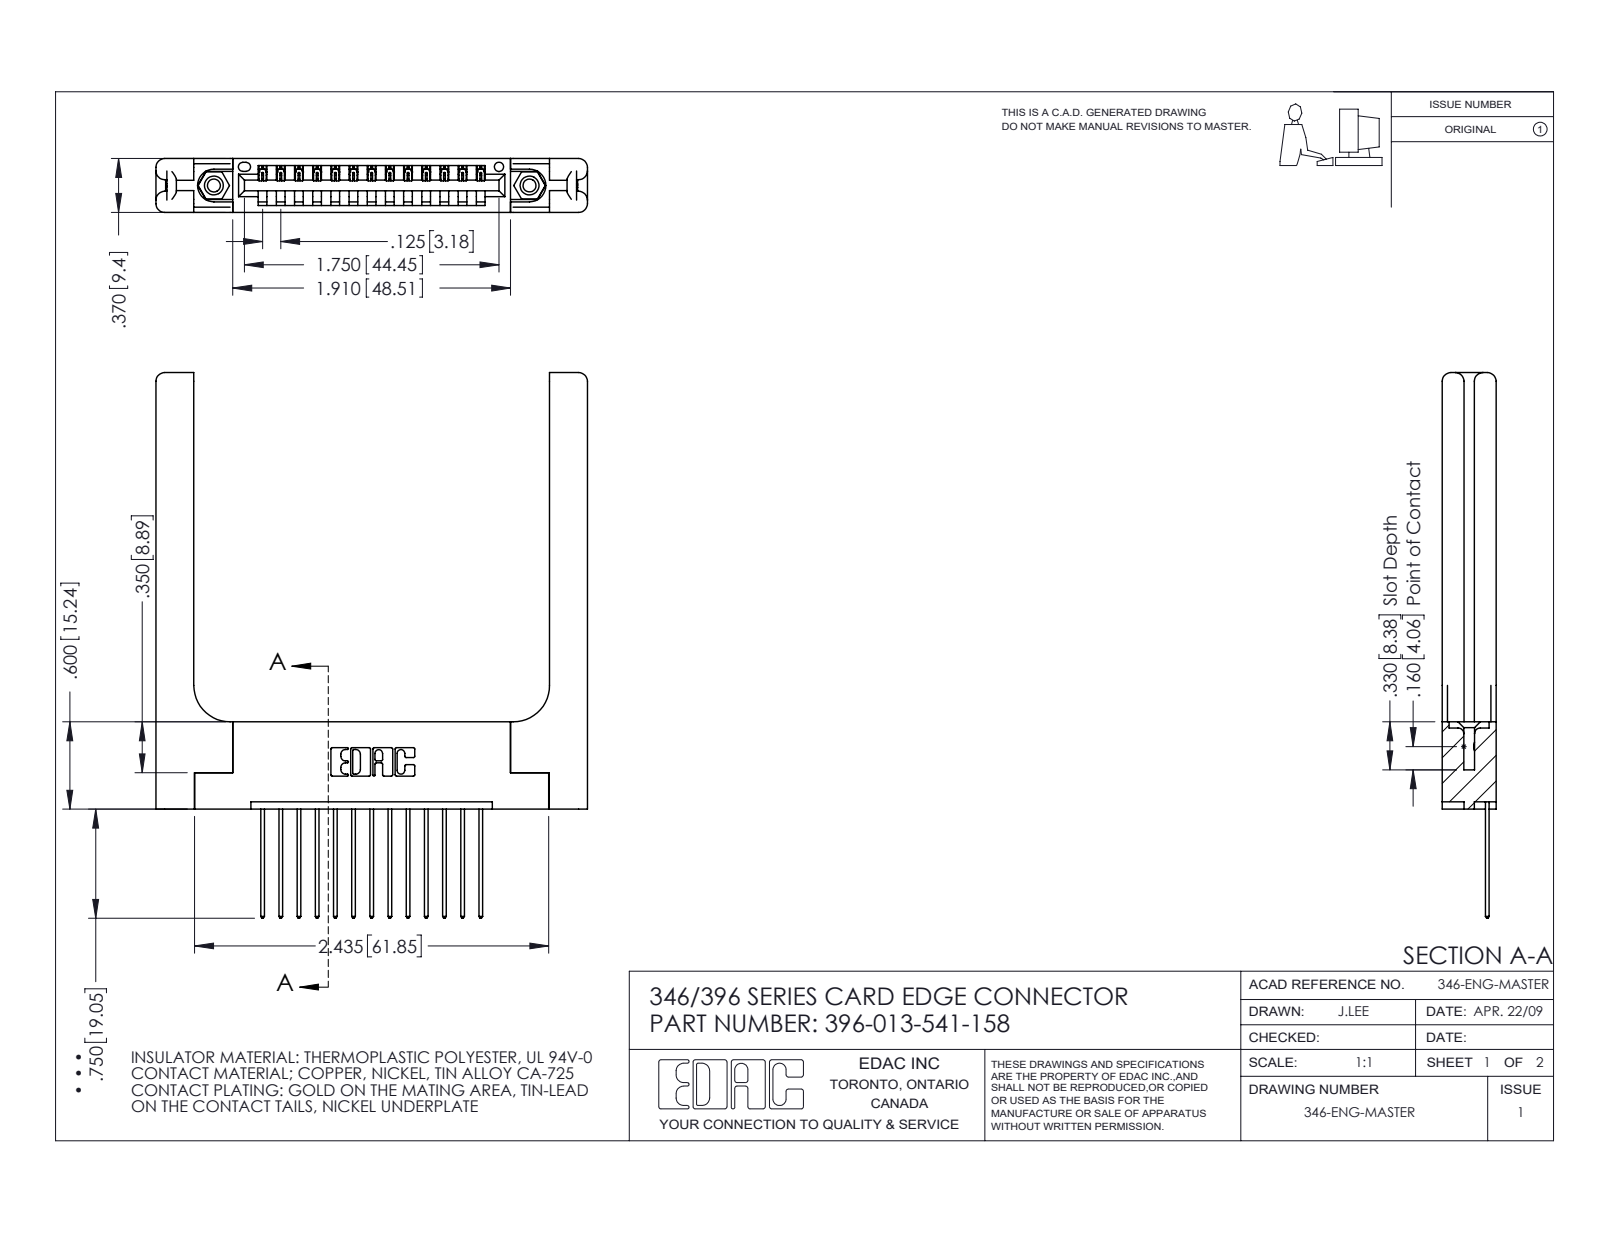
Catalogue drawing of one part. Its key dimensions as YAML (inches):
part_name: "345-292-001_345-293-141; 346 Part_Flush Mounting Lugs - 0.156 Dia-TH; 396-013-541-158; 345-250-001_345-250-001-102 (+1 more)"
step_written_by: "SolidWorks 2016 (CONFIG_CONTROL_DESIGN)"
units: inches
bodies: {solids: 18, faces: 1132, planar: 744, cylindrical: 328, other: 60}
overall_size: [3.75, 2.966, 0.37]
volume: 0.889
surface_area: 21.59
round_holes:
  - {diameter: 0.089, count: 2}
  - {diameter: 0.125, count: 2}
  - {diameter: 0.156, count: 2}
  - {diameter: 0.064, count: 1}
round_bosses_or_shafts:
  - {diameter: 0.155, count: 2}
partial_cylinders:
  - {radius: 0.006, count: 26}
  - {radius: 0.01, count: 26}
  - {radius: 0.01, count: 22}
  - {radius: 0.06, count: 16}
  - {radius: 0.007, count: 6}
  - {radius: 0.031, count: 6}
  - {radius: 0.026, count: 3}
  - {radius: 0.03, count: 2}
face_to_face_distances: [0.37, 0.15, 0.072, 0.148, 0.048, 0.322, 0.22, 0.25, 0.102, 0.173]
hole_center_spacings: [0.246, 1.964, 2.17]
